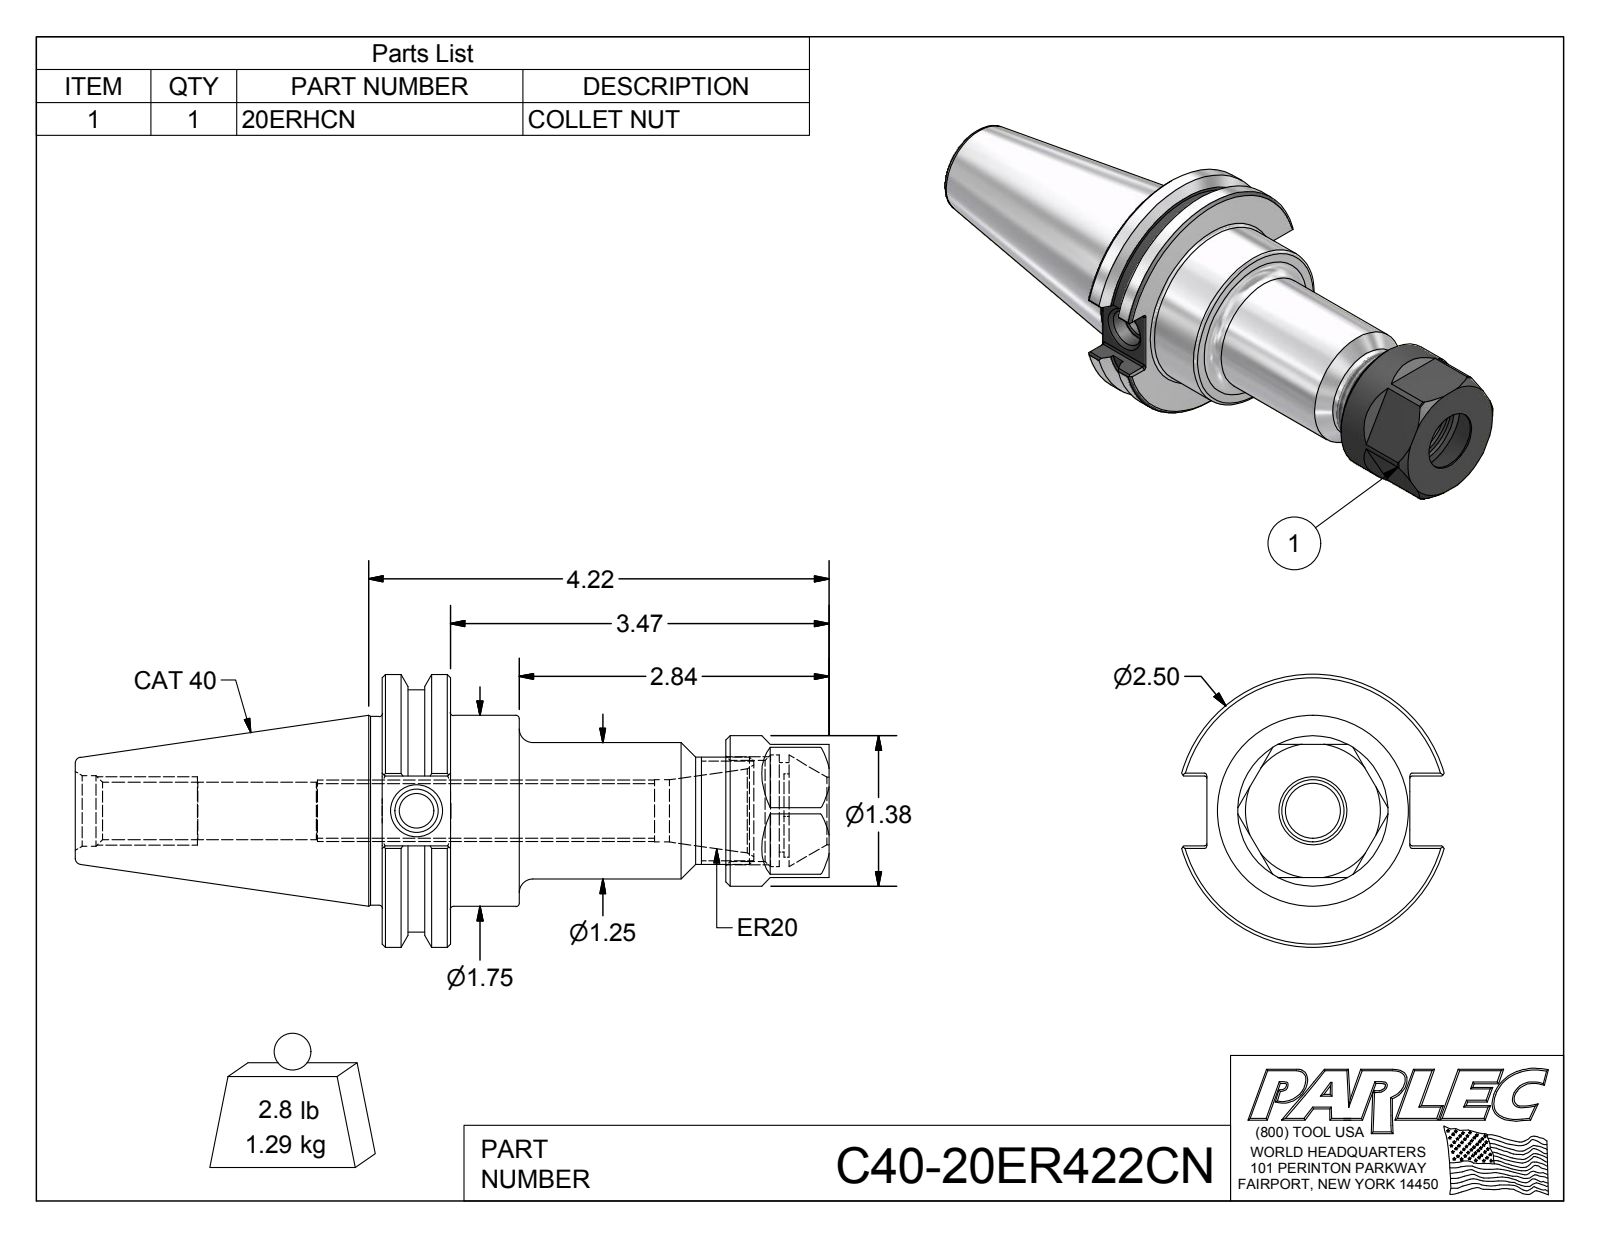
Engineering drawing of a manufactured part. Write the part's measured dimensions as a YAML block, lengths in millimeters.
part_name: "C40-20ER422CN; C40-20ER4-1; 20ERHCN"
step_written_by: "Autodesk Inventor 2012 (AUTOMOTIVE_DESIGN)"
units: millimeters
bodies: {solids: 2, faces: 126, planar: 50, cylindrical: 35, other: 41}
overall_size: [175.5, 63.5, 61]
volume: 164500
surface_area: 35870
round_holes:
  - {diameter: 8, count: 1}
  - {diameter: 10.1, count: 1}
  - {diameter: 12.8, count: 1}
  - {diameter: 13.3, count: 1}
  - {diameter: 13.4, count: 1}
  - {diameter: 14.5, count: 1}
  - {diameter: 15.7, count: 1}
  - {diameter: 16.5, count: 1}
  - {diameter: 20.8, count: 1}
  - {diameter: 23.5, count: 1}
  - {diameter: 26, count: 1}
round_bosses_or_shafts:
  - {diameter: 63.5, count: 1}
  - {diameter: 56.4, count: 1}
  - {diameter: 44.5, count: 1}
  - {diameter: 43.9, count: 1}
  - {diameter: 35, count: 1}
  - {diameter: 31.8, count: 1}
  - {diameter: 25, count: 1}
partial_cylinders:
  - {radius: 0.5, count: 12}
  - {radius: 10.7, count: 1}
face_to_face_distances: [15.9, 31, 104, 88.1, 80, 64.1, 24, 31.9, 16, 48.1]
hole_center_spacings: [0.9]
